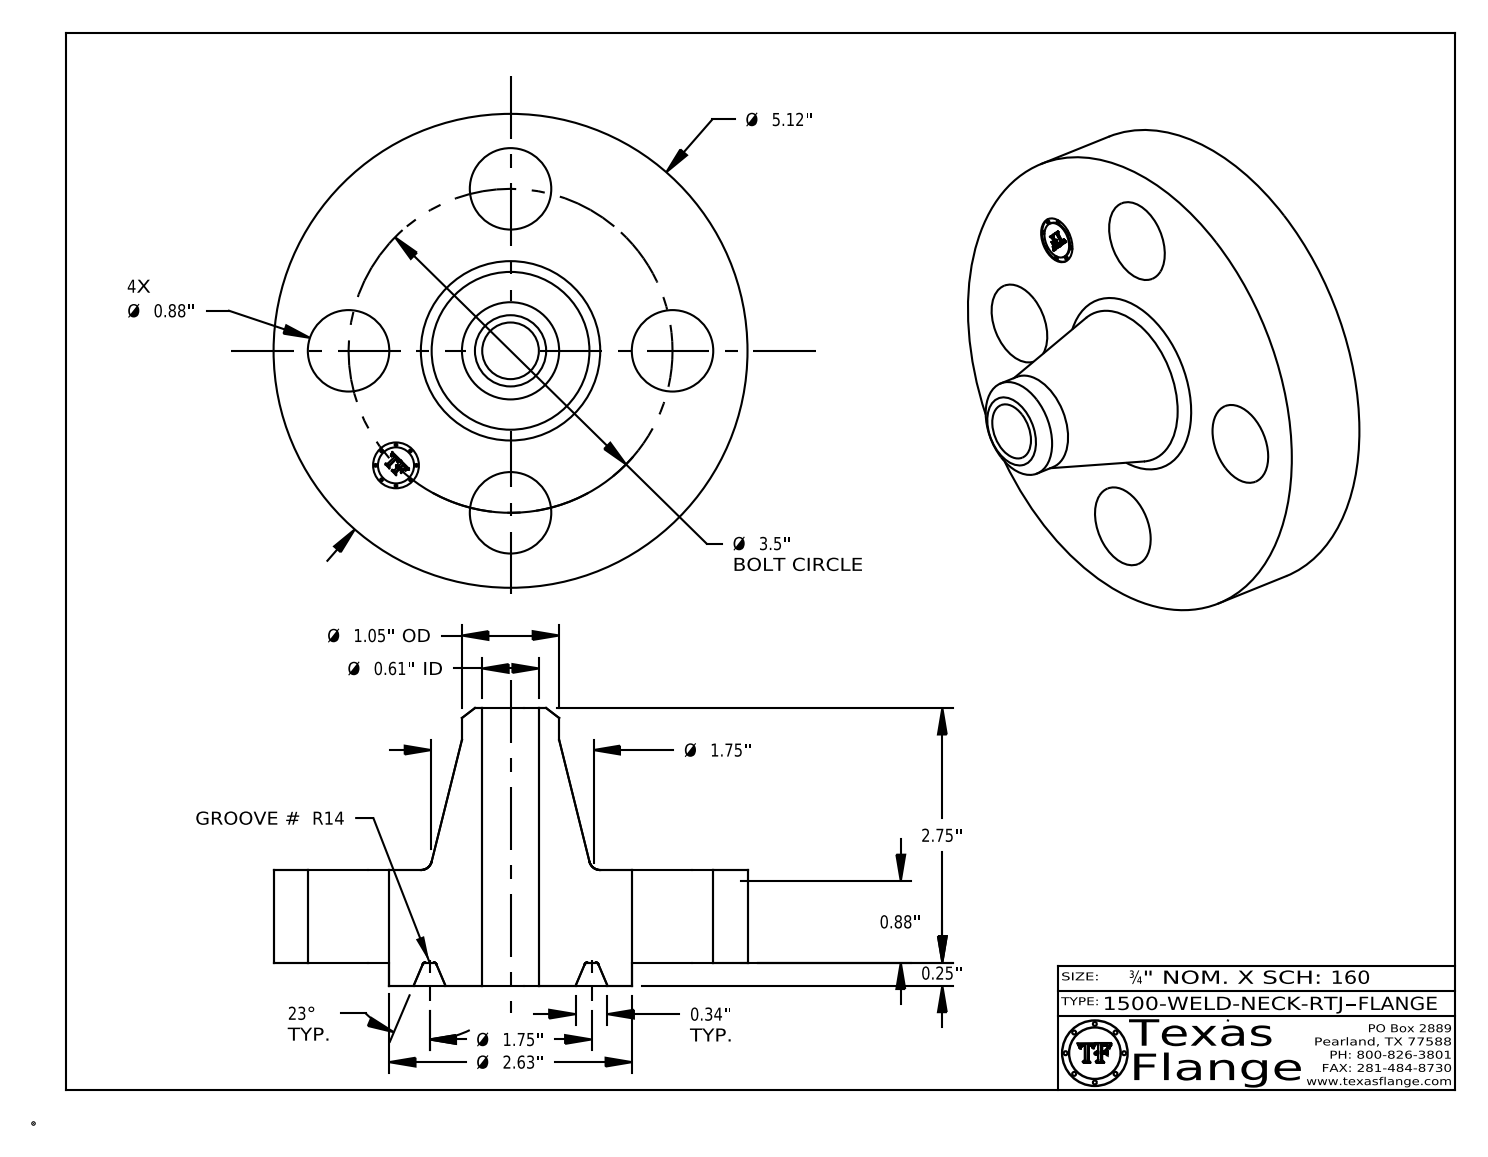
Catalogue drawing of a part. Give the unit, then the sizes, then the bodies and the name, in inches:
Units: inches
Overall size (bounding box): 5.12 × 5.12 × 3
Round holes (diameter × count): ⌀0.88 ×4, ⌀0.495 ×1, ⌀0.612 ×1
Round bosses / shafts (diameter × count): ⌀0.03 ×8, ⌀5.12 ×1, ⌀2.625 ×1, ⌀1.05 ×1, ⌀0.39 ×1
Main face-to-face distances: 1, 0.25, 1.25, 3, 2.75, 1.75, 0.015, 1.235, 0.985, 1.765
Hole centre spacings: 1.75, 2.475, 1.339, 3.233, 3.5
Volume: 20.79 in³ · Surface area: 78.12 in²
Bodies: 1 solid, 425 faces (371 planar, 40 cylindrical, 14 other)
Part name (STEP PRODUCT): 1500-WELD-NECK-RTJ
STEP written by: CATIA V5 STEP AP214 (AUTOMOTIVE_DESIGN)
